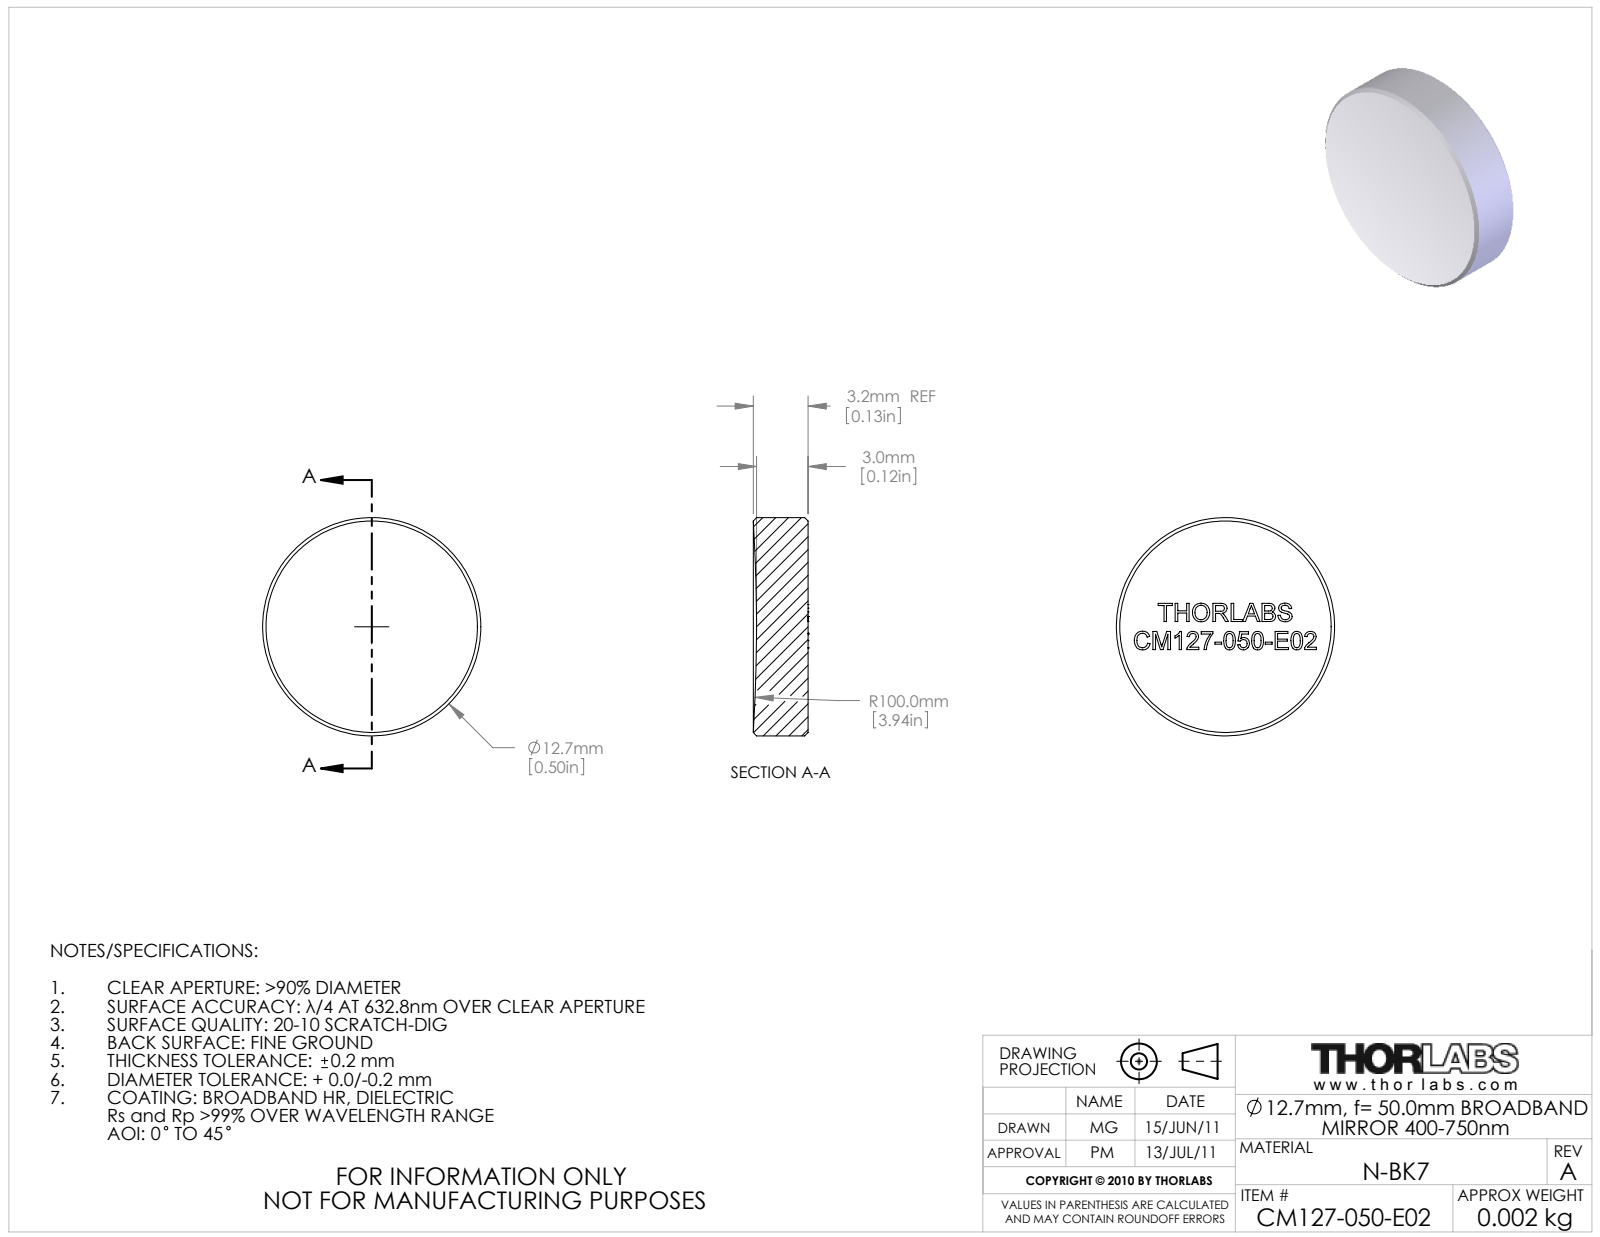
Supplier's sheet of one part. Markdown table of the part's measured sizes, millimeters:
| quantity | value |
| --- | --- |
| part name | 22625-E0W |
| STEP written by | SolidWorks 2011 (AUTOMOTIVE_DESIGN) |
| units | millimeters |
| bodies | 0 solids, 42 faces (31 planar, 2 cylindrical, 9 other) |
| overall size | 12.7 × 12.7 × 3.19 |
| round bosses / shafts (diameter × count) | 12.7 × 1 |
